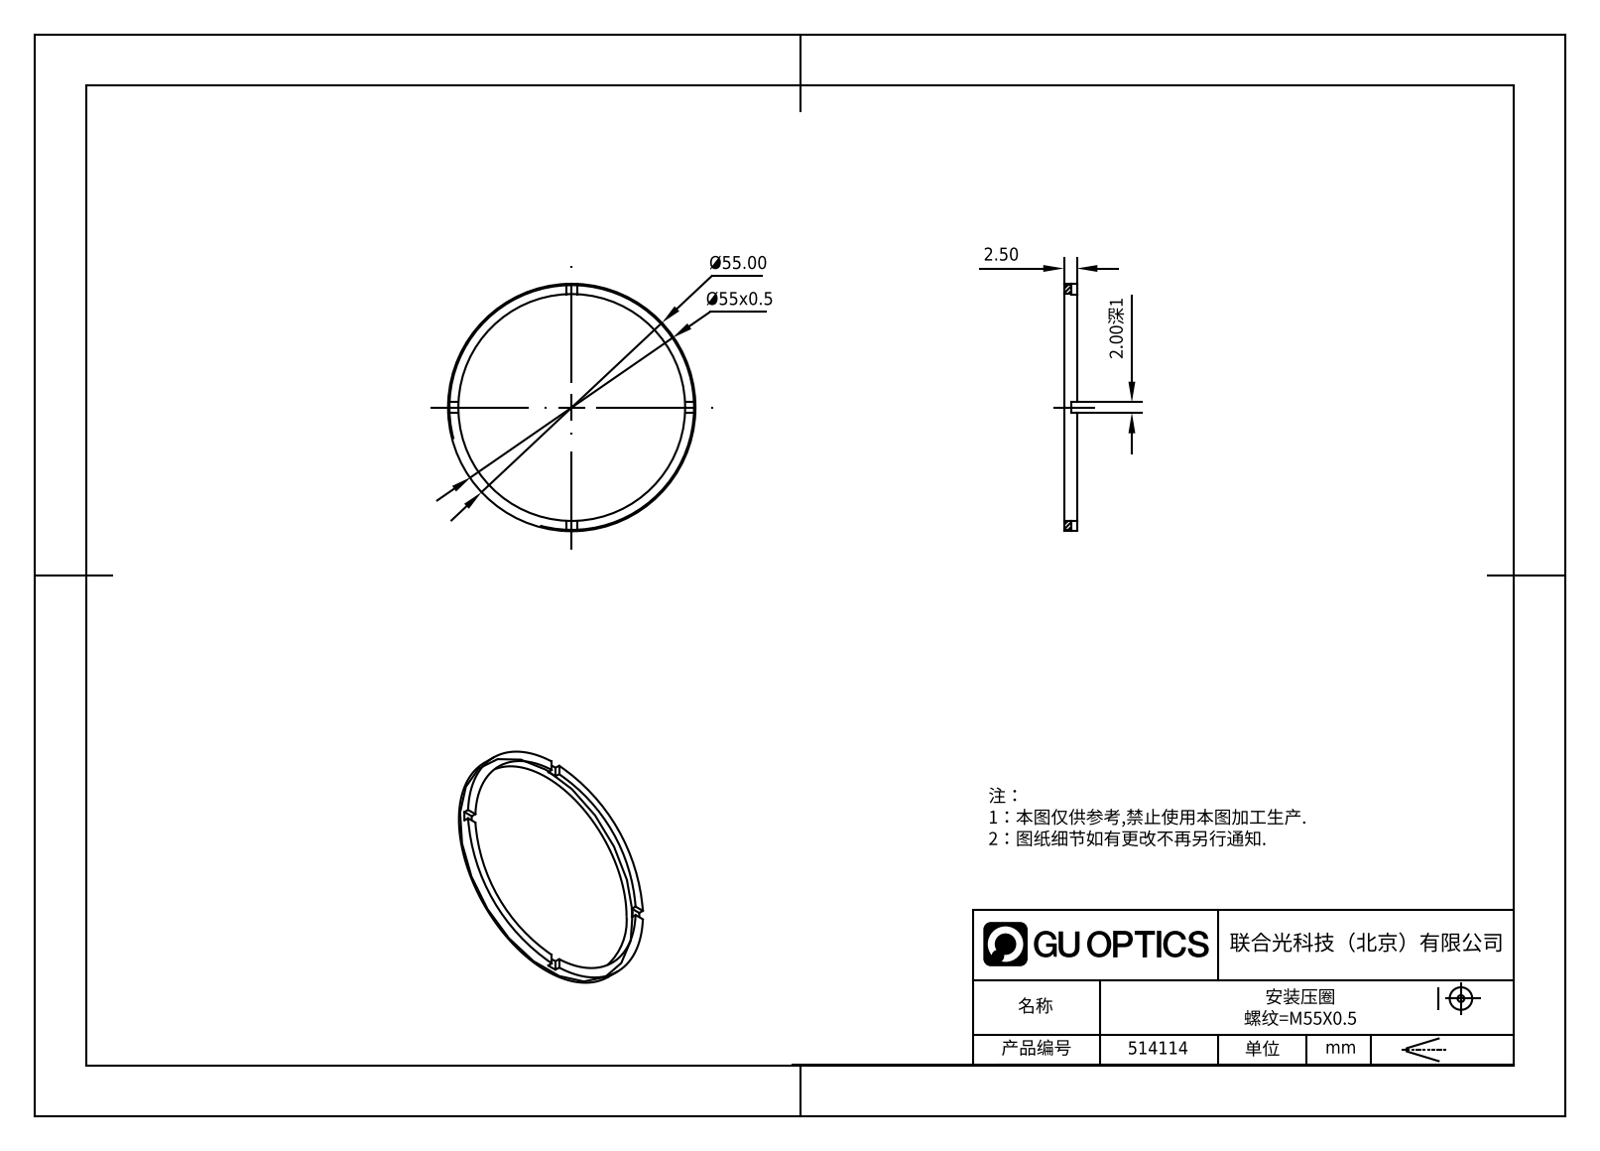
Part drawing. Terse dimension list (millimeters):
name: 514114
written by: SolidWorks 2020 (CONFIG_CONTROL_DESIGN)
unit: mm
bodies: 1 solid, 21 faces (17 planar, 4 cylindrical, 0 other)
size: 55 × 55 × 2.5
volume: 1 011 mm³; area: 1 653 mm²
holes: 1× ⌀50
bosses: 1× ⌀55
face distances: 2.5, 1.5, 1, 2
